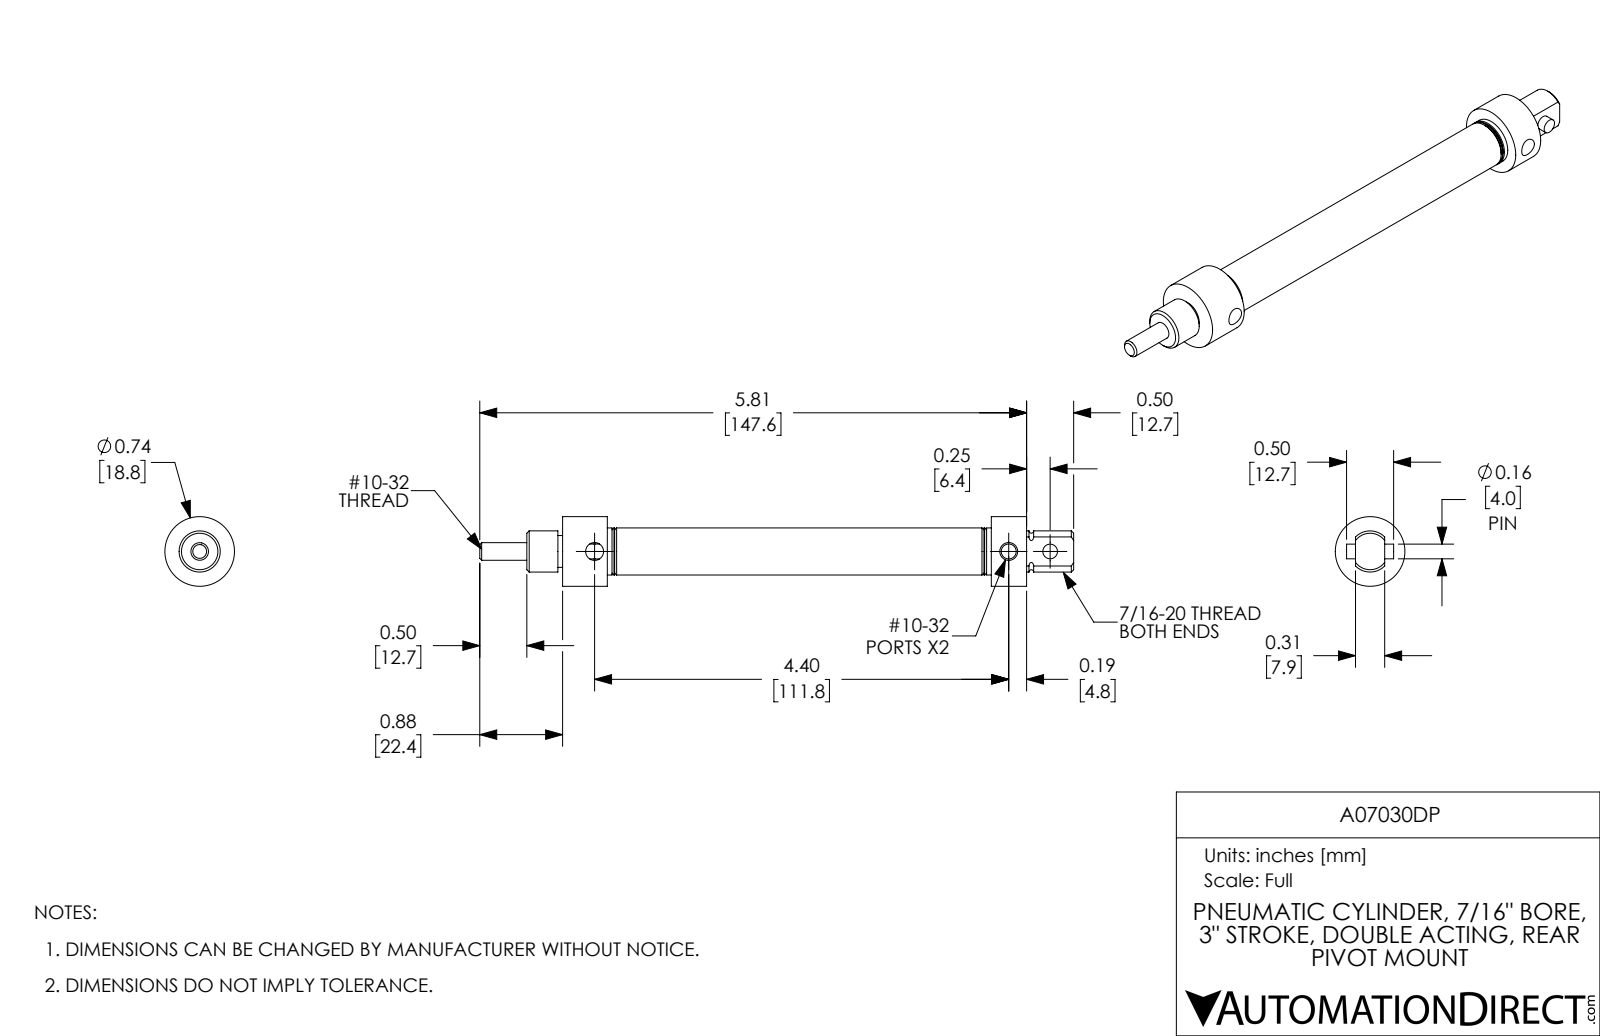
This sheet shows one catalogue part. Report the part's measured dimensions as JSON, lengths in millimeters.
{"part_name": "A07030DP-Pin; A07030DP-MainBody; A07030DP; A07030DP-Rod", "step_written_by": "SolidWorks 2017 (AUTOMOTIVE_DESIGN)", "units": "millimeters", "bodies": {"solids": 3, "faces": 89, "planar": 23, "cylindrical": 44, "other": 22}, "overall_size": [160.3, 18.8, 18.8], "volume_mm3": 14900, "surface_area_mm2": 13760, "round_holes": [[4, 2], [4.8, 2], [4, 1], [4.7, 1]], "round_bosses_or_shafts": [[18.8, 1], [12.7, 1], [11.1, 1], [8.6, 1]], "face_to_face_distances": [18.2, 107.1, 125.2, 115.7, 12.7, 113.2, 95, 12.1, 9.5, 8.6], "hole_center_spacings": [11.2, 111.8, 122.9]}
